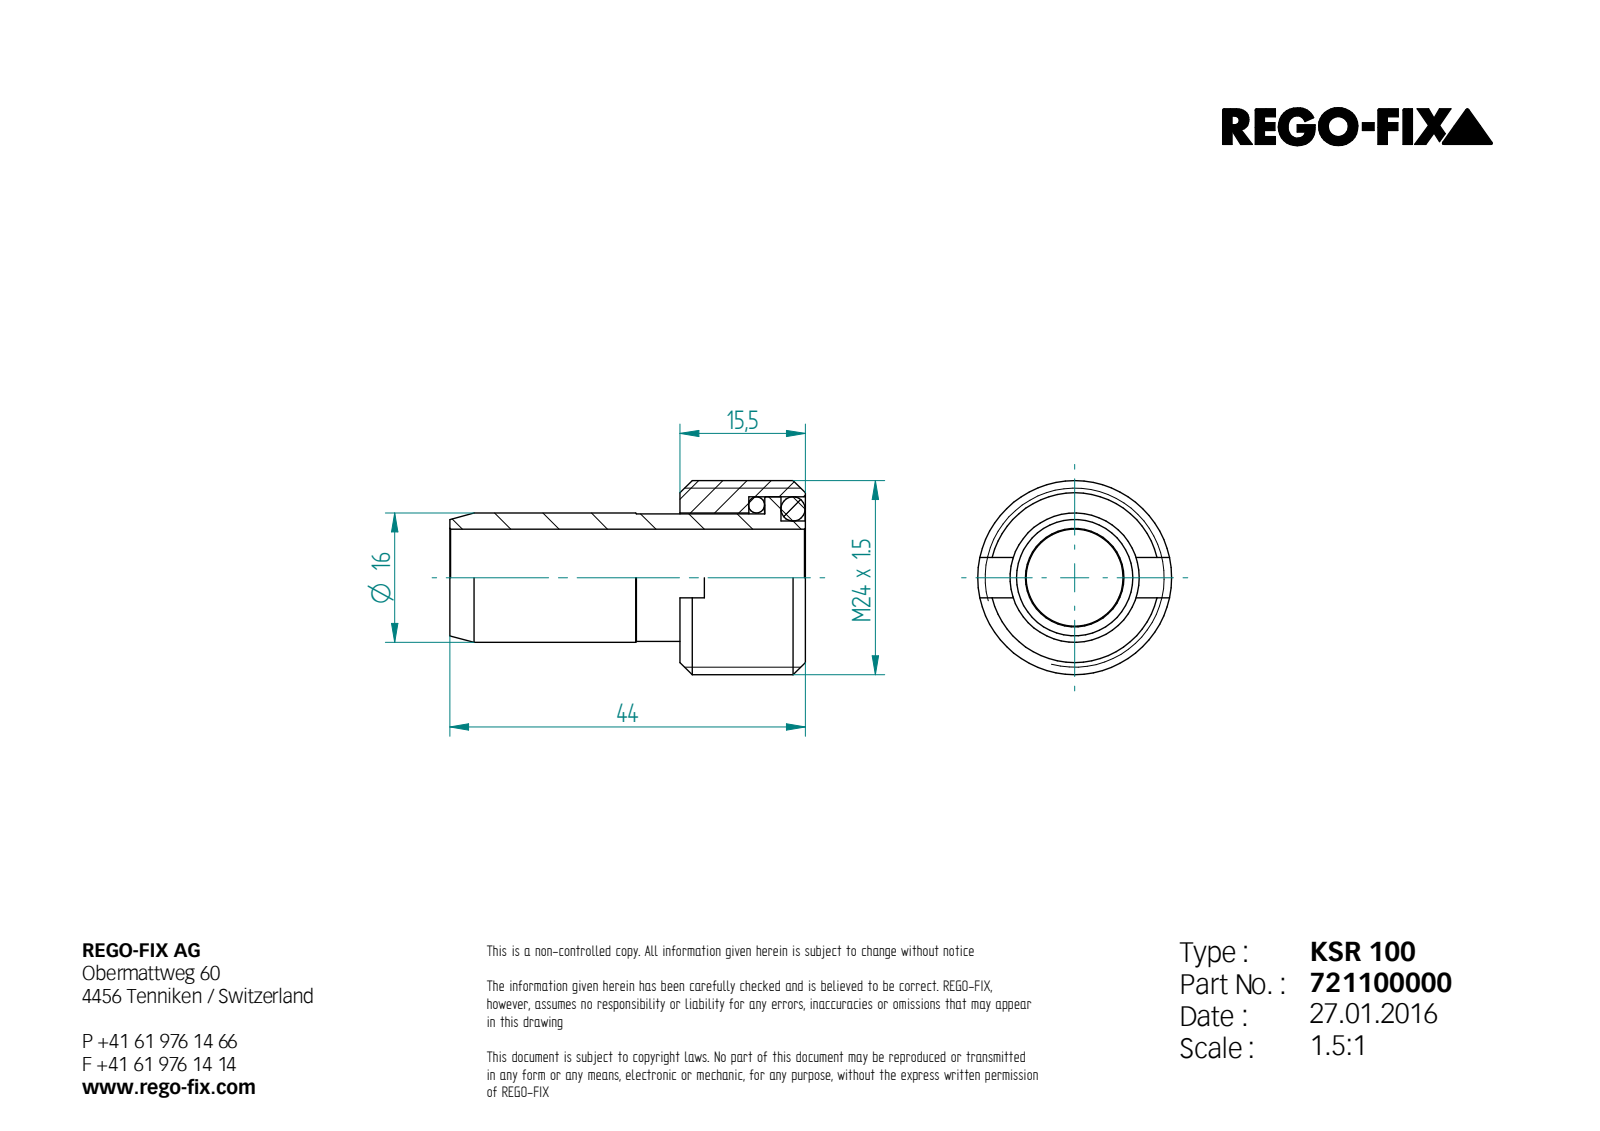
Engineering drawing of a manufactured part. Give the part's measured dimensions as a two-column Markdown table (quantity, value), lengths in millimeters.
| quantity | value |
| --- | --- |
| part name | 0012526; 0012527; 0012529; 0012530 |
| STEP written by | Unknown (AUTOMOTIVE_DESIGN) |
| units | millimeters |
| bodies | 4 solids, 32 faces (14 planar, 8 cylindrical, 10 other) |
| overall size | 44 × 24 × 24 |
| volume | 7 203 mm³ |
| surface area | 7 479 mm² |
| round holes (diameter × count) | 12 × 1, 16 × 1, 20 × 1 |
| round bosses / shafts (diameter × count) | 24 × 1, 15.8 × 1, 14 × 1 |
| main face-to-face distances | 2, 12.5, 8.5, 4, 10.5, 3, 5, 15.5, 7, 28.5 |
